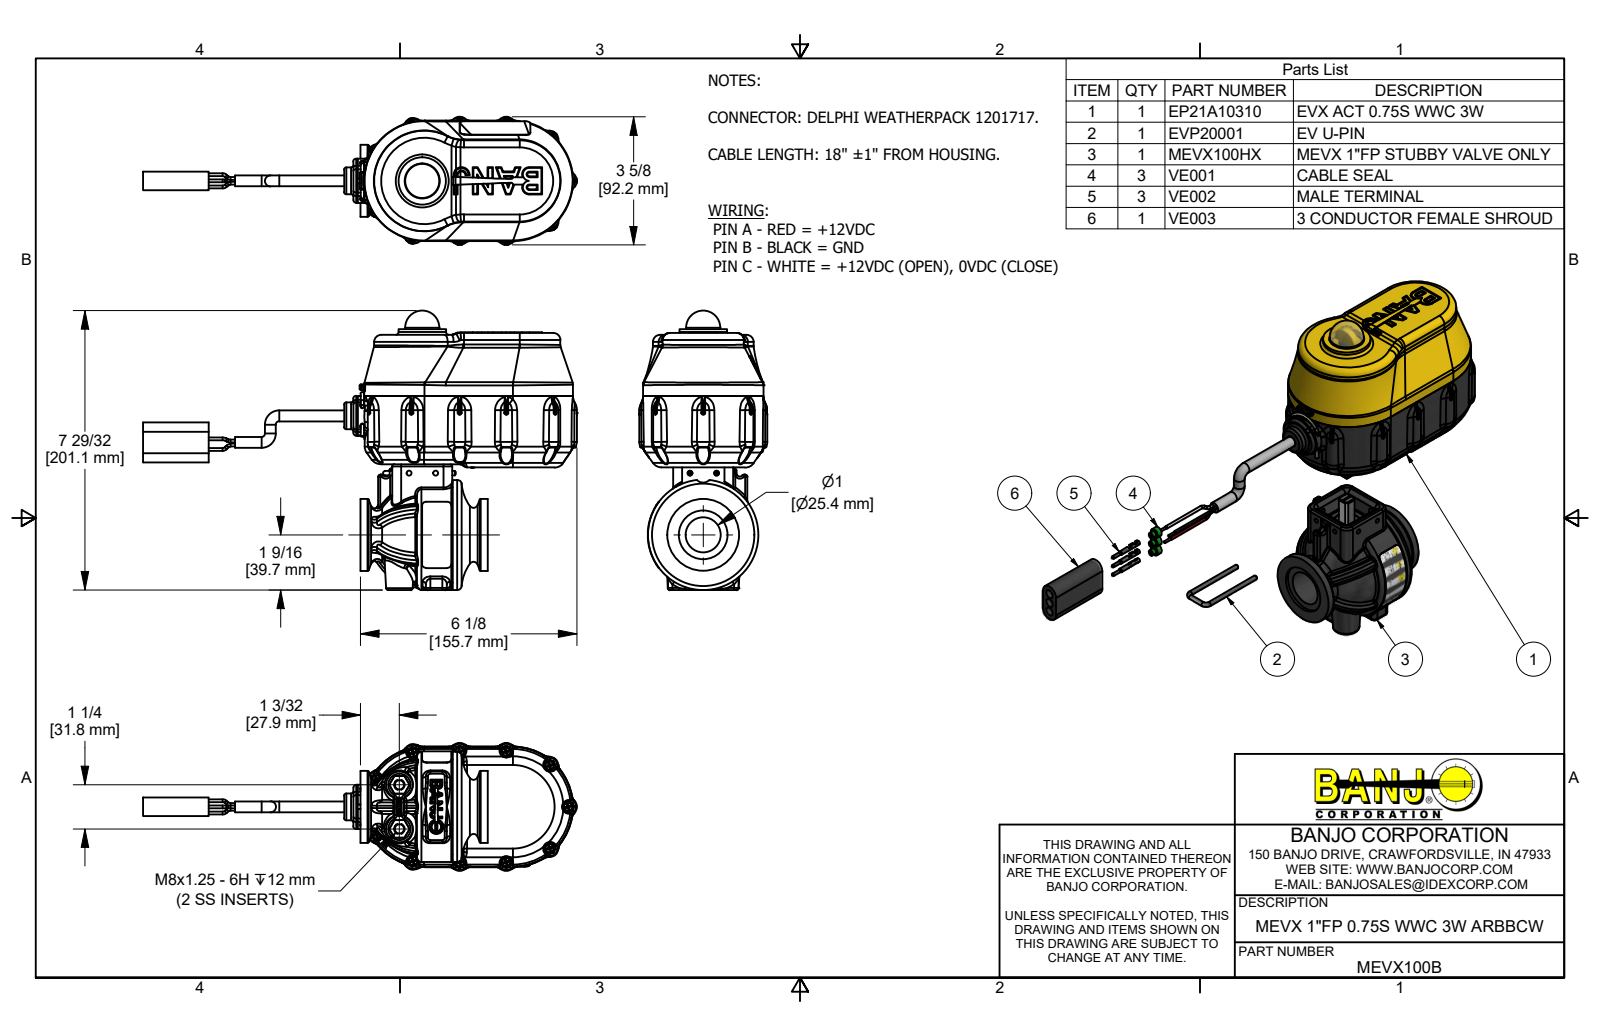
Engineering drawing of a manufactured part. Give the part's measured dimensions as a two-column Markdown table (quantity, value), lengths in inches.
| quantity | value |
| --- | --- |
| part name | MEVX100B; EP21A10310; EP21A; EVP25101 (+8 more) |
| STEP written by | Autodesk Inventor 2019 (AUTOMOTIVE_DESIGN) |
| units | inches |
| bodies | 91 solids, 11094 faces (3076 planar, 3131 cylindrical, 4887 other) |
| overall size | 13.21 × 7.916 × 3.63 |
| volume | 47.07 in³ |
| surface area | 543.2 in² |
| round holes (diameter × count) | 0.095 × 11, 0.15 × 11, 0.08 × 7, 0.15 × 7, 0.135 × 5, 0.107 × 4, 0.126 × 4, 0.136 × 4, 0.148 × 4, 0.17 × 4, 0.25 × 4, 0.049 × 3 |
| round bosses / shafts (diameter × count) | 0.08 × 18, 0.25 × 17, 0.14 × 11, 0.108 × 11, 0.085 × 11, 0.058 × 6, 0.27 × 4, 0.219 × 4 |
| partial cylindrical surfaces (radius × count) | 0.013 × 180, 0.04 × 145, 0.01 × 84, 0.02 × 71, 0.005 × 54, 0.06 × 46, 0.08 × 28, 0.03 × 26 |
| main face-to-face distances | 0.1, 2.565, 0.211, 0.06, 0.151, 1.896, 1.685, 1.836, 2.465, 0.78 |
| hole center spacings | 1.283, 2.656, 0.75, 1.662, 1.79, 2.73, 2.967, 3.45 |
